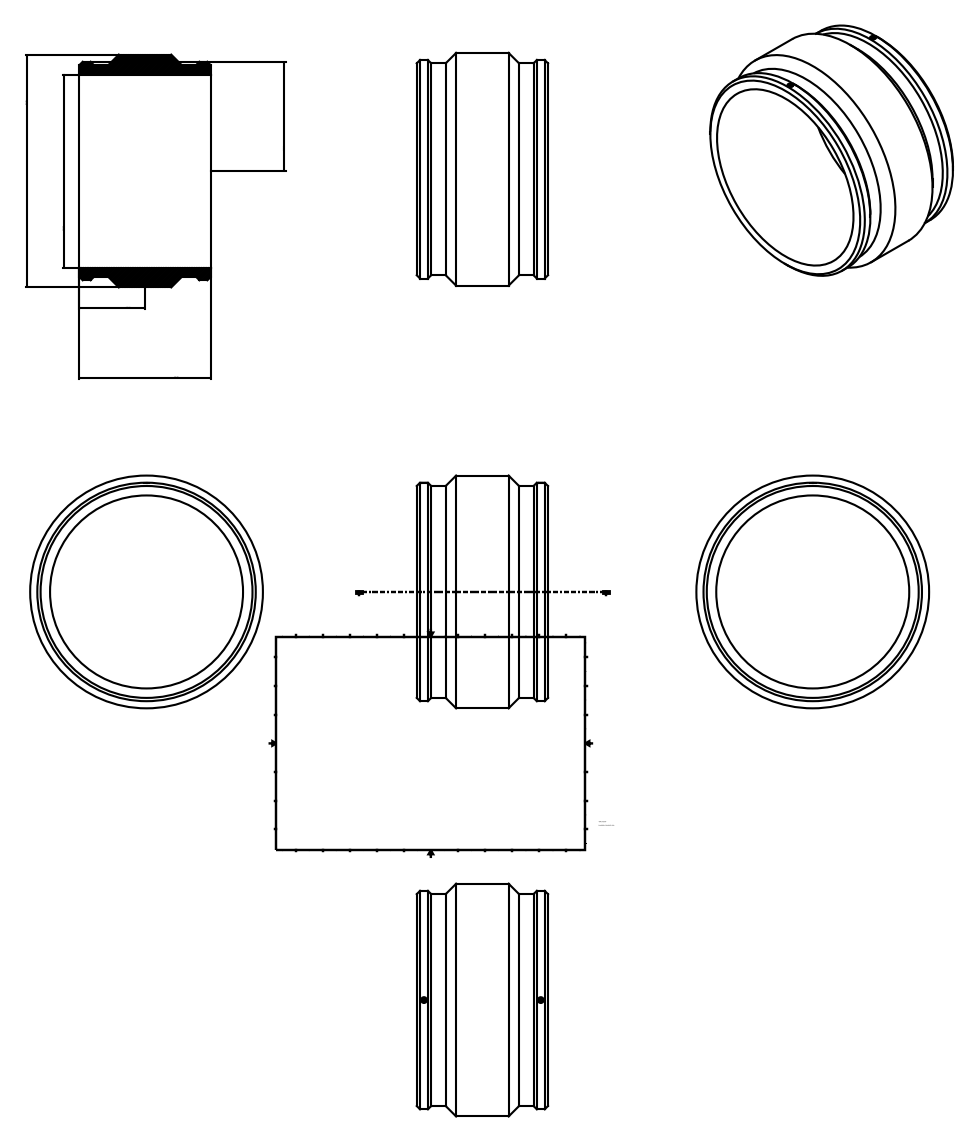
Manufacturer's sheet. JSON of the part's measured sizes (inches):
{"part_name": "490103500", "step_written_by": "Autodesk Inventor 2015 (AUTOMOTIVE_DESIGN)", "units": "inches", "bodies": {"solids": 1, "faces": 28, "planar": 8, "cylindrical": 14, "other": 6}, "overall_size": [23.74, 23.74, 13.386], "volume_in3": 1375, "surface_area_in2": 2012, "round_holes": [[0.394, 2], [19.685, 1]], "round_bosses_or_shafts": [[0.591, 2], [0.157, 2], [23.74, 1], [22.283, 1], [21.615, 1]], "face_to_face_distances": [13.386, 0.551, 0.433, 0.118], "hole_center_spacings": [11.913]}
